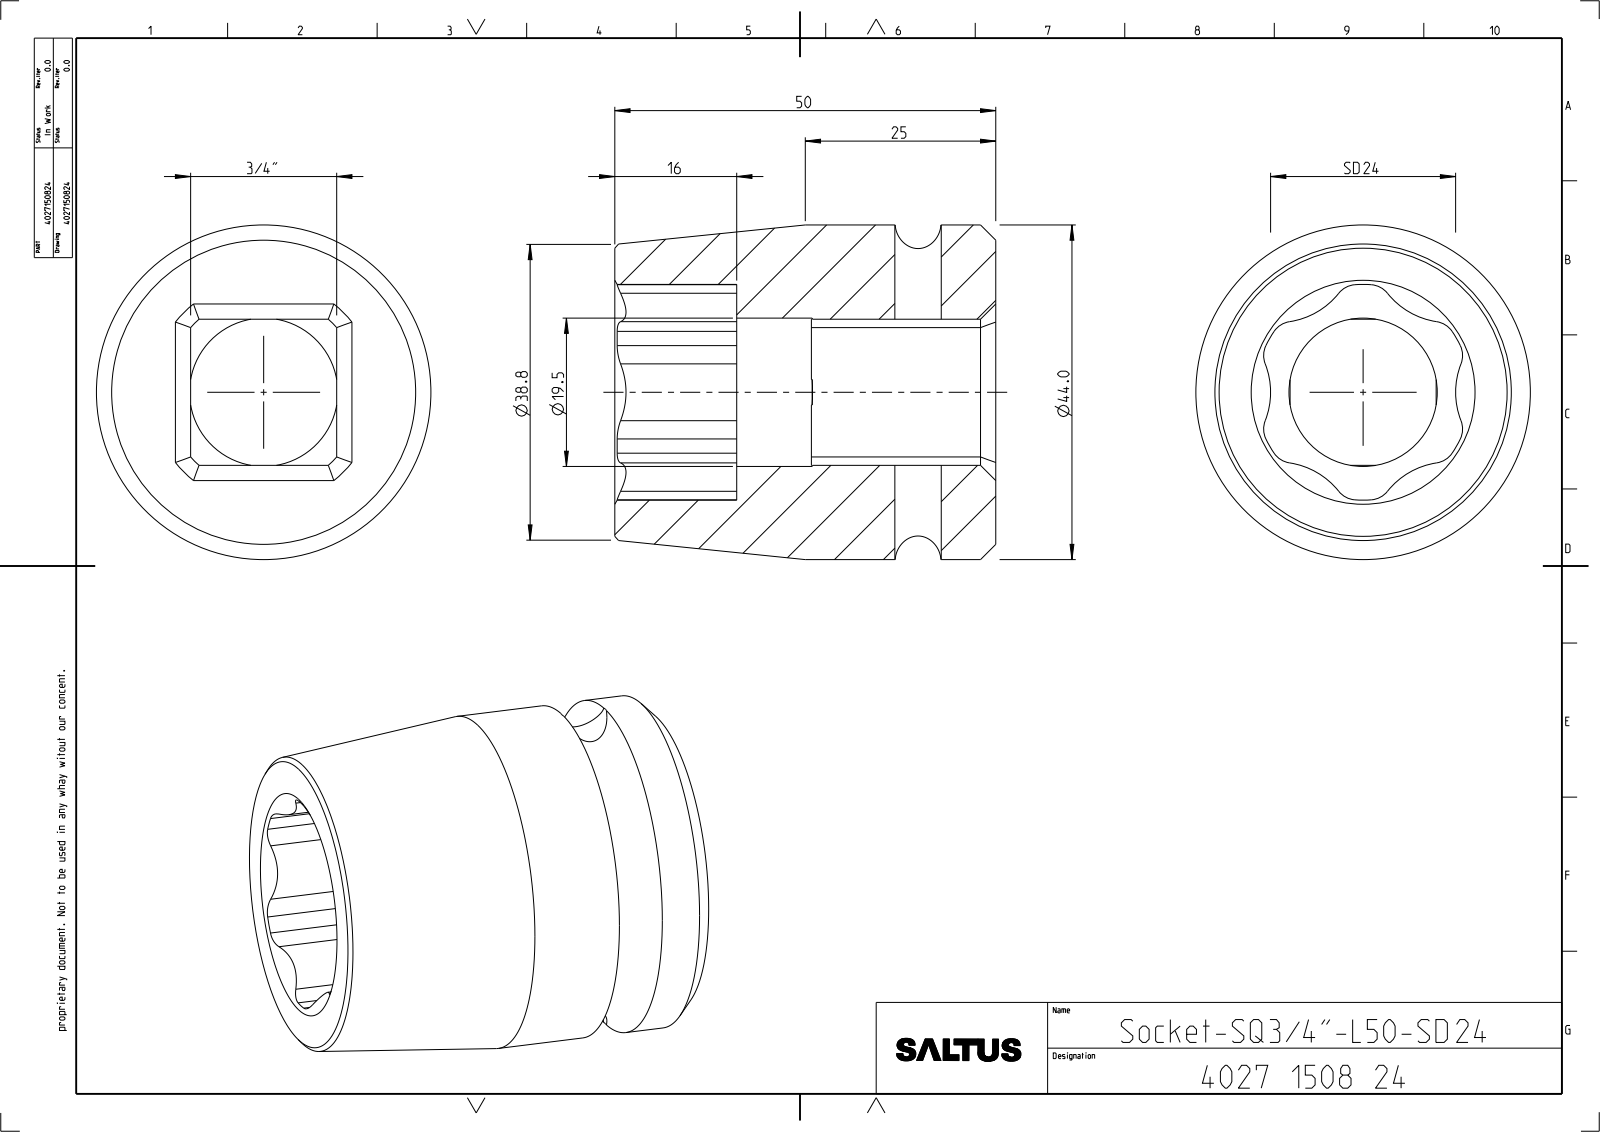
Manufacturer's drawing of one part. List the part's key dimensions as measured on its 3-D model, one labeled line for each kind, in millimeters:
Part name (STEP PRODUCT): 4027150824
STEP written by: CREO PARAMETRIC BY PTC INC, 2022414 (CONFIG_CONTROL_DESIGN)
Units: millimetres
Bodies: 1 solid, 71 faces (15 planar, 38 cylindrical, 18 other)
Overall size (bounding box): 50 × 43.9 × 43.9
Volume: 48 104 mm³ · Surface area: 12 885 mm²
Round holes (diameter × count): ⌀6.09 ×1, ⌀19.46 ×1
Round bosses / shafts (diameter × count): ⌀43.9 ×1
Partial cylindrical surfaces — rounded edges, fillets, slot ends (radius × count): R3 ×12, R10.2 ×6, R12.8 ×1, R14.15 ×1
Main face-to-face distances: 19.18, 50, 34, 16, 24.2, 9.8, 25.8
